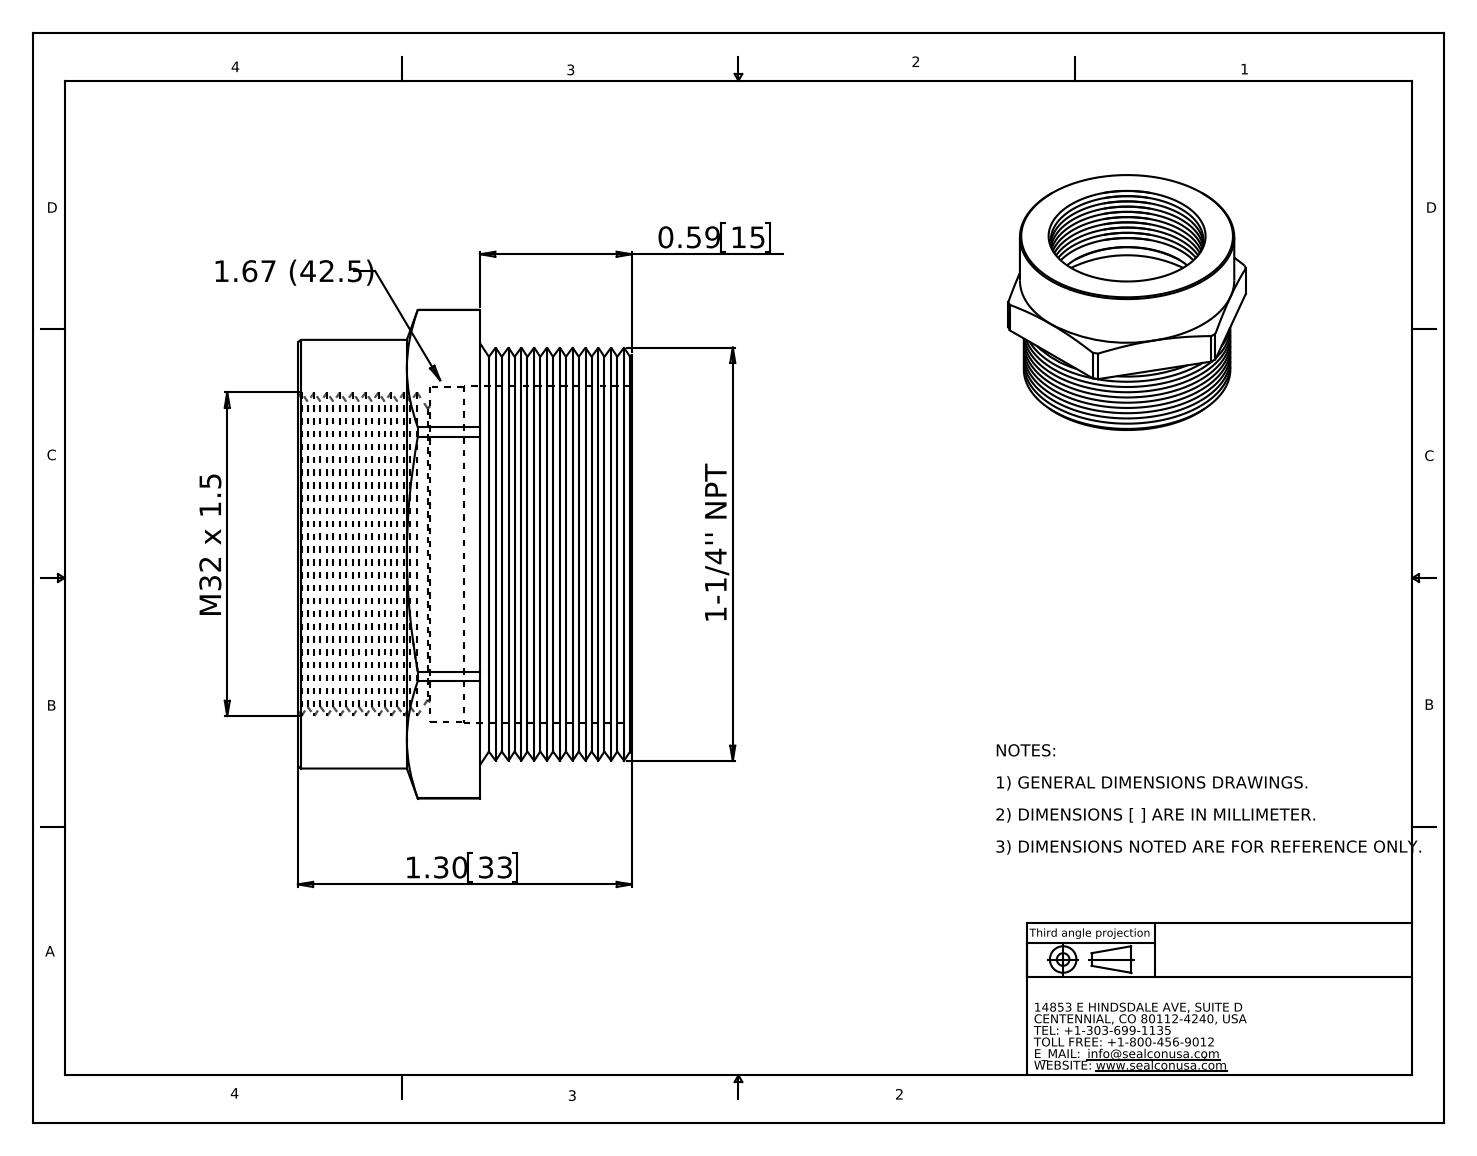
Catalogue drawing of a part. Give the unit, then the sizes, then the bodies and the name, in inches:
Units: inches
Overall size (bounding box): 1.904 × 1.67 × 1.3
Round holes (diameter × count): ⌀1.304 ×1, ⌀1.312 ×1
Round bosses / shafts (diameter × count): ⌀1.67 ×1
Partial cylindrical surfaces — rounded edges, fillets, slot ends (radius × count): R0.952 ×1
Main face-to-face distances: 1.67, 1.3, 0.59, 0.71, 0.785, 0.195, 0.515, 0.655, 0.065, 0.13
Volume: 1.102 in³ · Surface area: 17.92 in²
Bodies: 1 solid, 123 faces (11 planar, 13 cylindrical, 99 other)
Part name (STEP PRODUCT): AT-5432-BR
STEP written by: SolidWorks 2008 (CONFIG_CONTROL_DESIGN)
